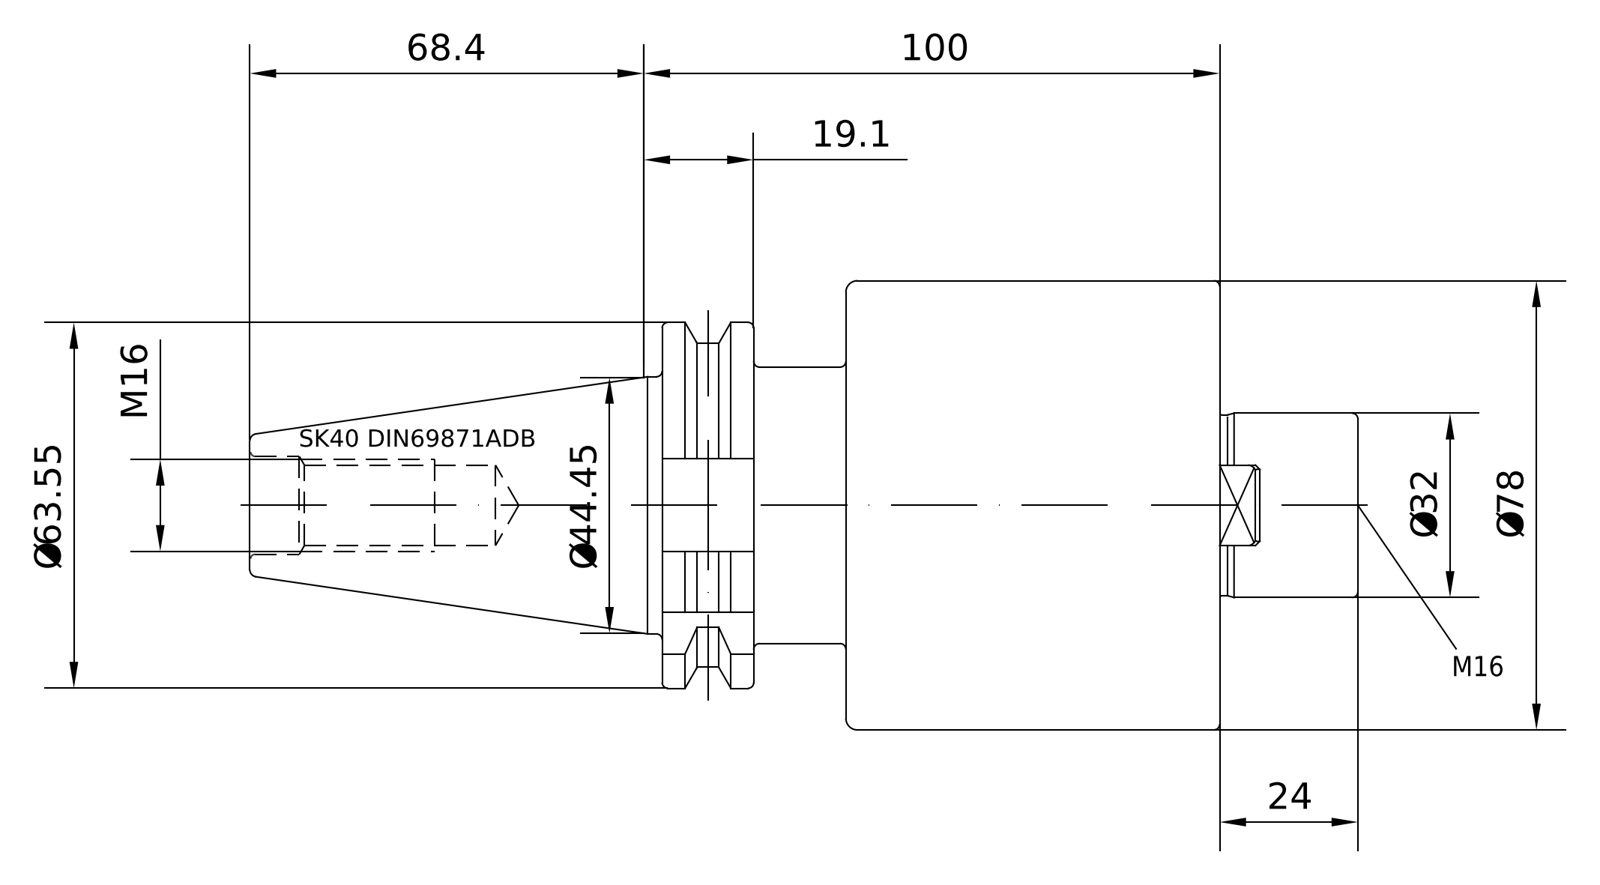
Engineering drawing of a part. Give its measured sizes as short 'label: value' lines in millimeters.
name: 40-351-32
written by: PRO/ENGINEER BY PARAMETRIC TECHNOLOGY CORPORATION, 2010430 (CONFIG_CONTROL_DESIGN)
unit: mm
bodies: 1 solid, 119 faces (34 planar, 33 cylindrical, 52 other)
size: 192.25 × 78 × 78
volume: 460 251 mm³; area: 50 288 mm²
holes: 1× ⌀13.84, 1× ⌀14, 1× ⌀16, 1× ⌀17.01, 1× ⌀17.5
bosses: 1× ⌀78, 1× ⌀48, 1× ⌀43.75, 1× ⌀32, 1× ⌀16.01
rounds: 5× R1.35, 1× R28, 1× R31.76
face distances: 64.95, 31.85, 96.8, 15.85, 16, 80.95, 120.8, 104.95, 88.95, 24
